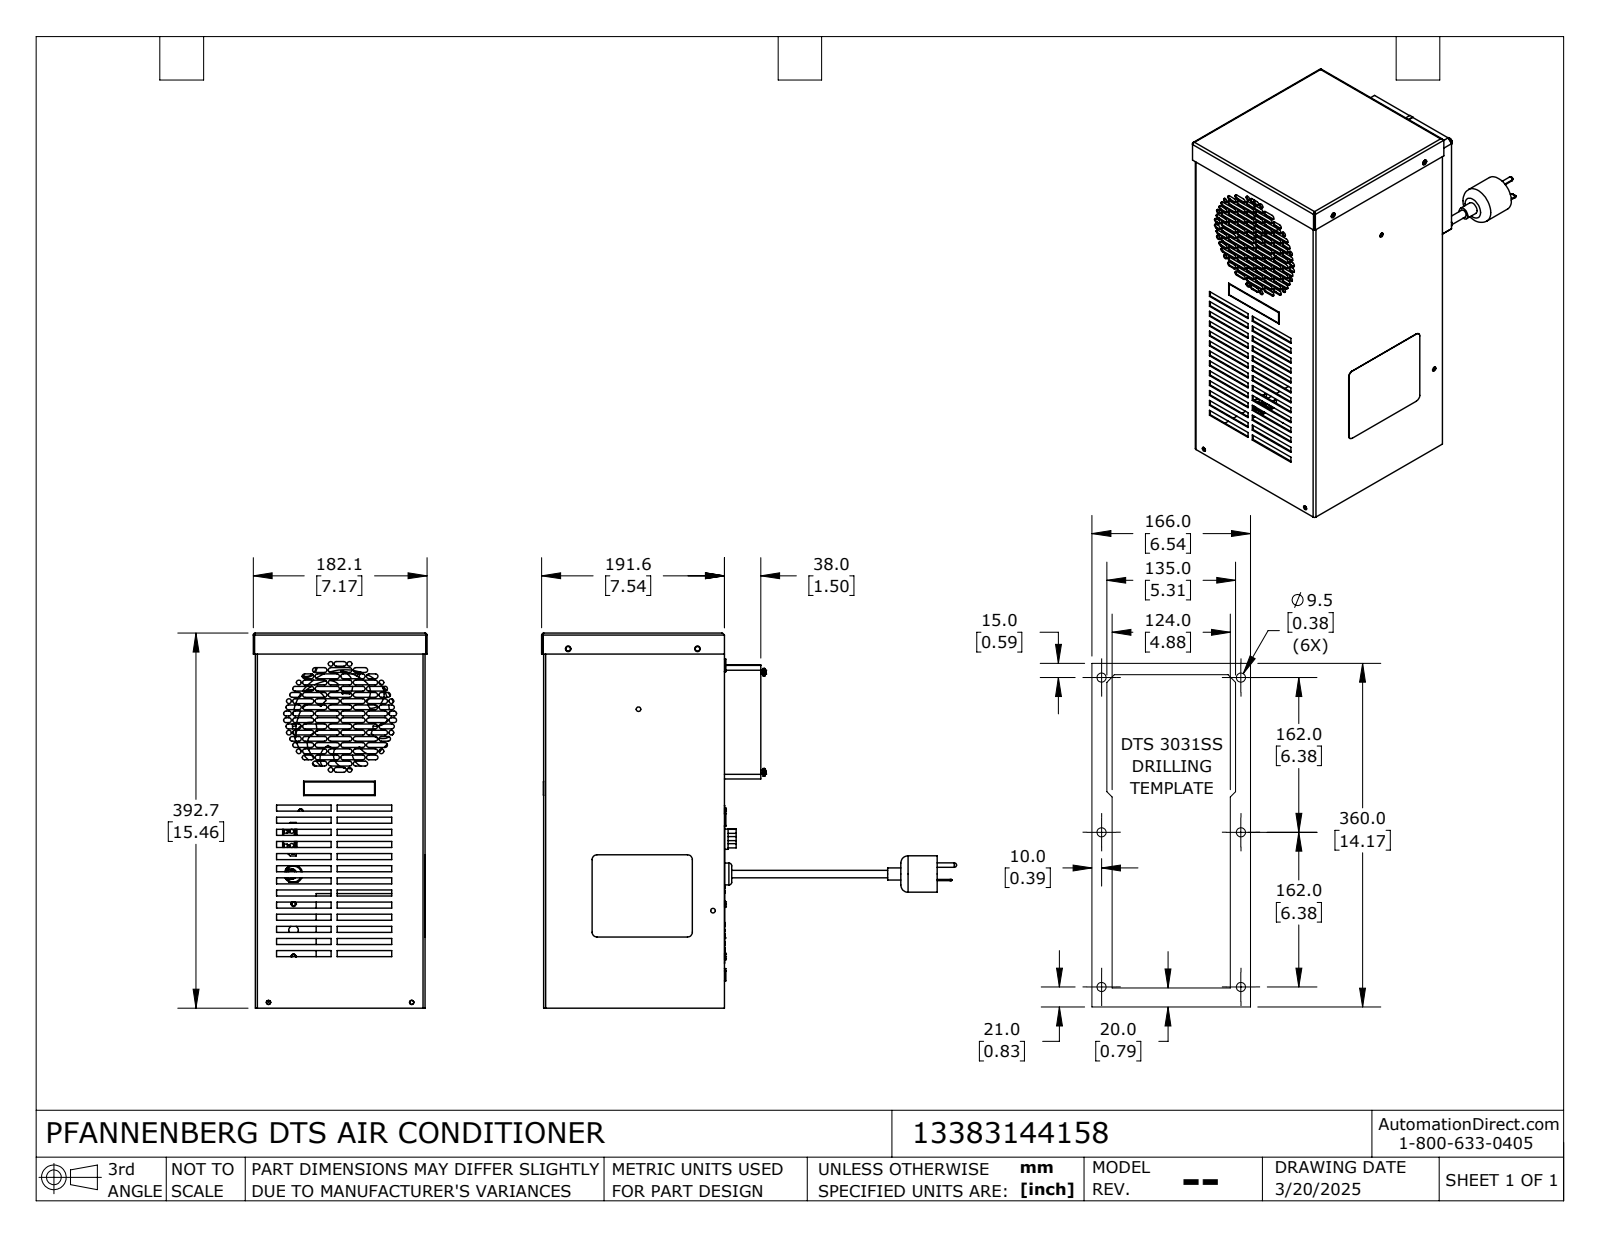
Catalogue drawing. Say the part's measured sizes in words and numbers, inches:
The part is named "13383144158_Default". Its 3-D file was written by "SolidWorks 2024 (CONFIG_CONTROL_DESIGN)". It is 28 solids with 3064 faces: 1547 planar, 697 cylindrical and 820 other. Overall it measures 17.116 by 15.461 by 7.168 inches. Its volume is 53.71 cubic inches and its surface area 1 449 square inches. Round holes: 17 of diameter 0.197, 9 of diameter 0.165, 9 of diameter 0.177, 6 of diameter 0.283, 5 of diameter 0.189, 5 of diameter 0.194, 3 of diameter 0.091, 3 of diameter 0.142, 3 of diameter 0.157, 3 of diameter 0.169, 2 of diameter 0.067, 2 of diameter 0.125. Round bosses or shafts: 6 of diameter 0.512, 4 of diameter 0.315, 3 of diameter 0.272, 3 of diameter 0.157, 2 of diameter 0.5, 1 of diameter 2.362, 1 of diameter 1.5, 1 of diameter 0.9. Partial cylindrical surfaces (rounded edges, fillets, slot ends): 140 of radius 0.098, 12 of radius 0.02, 8 of radius 0.036, 8 of radius 0.084, 7 of radius 0.039, 7 of radius 0.547, 7 of radius 0.597, 7 of radius 2.224. The main face-to-face distances are 0.048, 6.952, 7.41, 0.083, 6.87, 7, 6.905, 7.362, 7.457, 6.917. The hole center spacings are 0.291, 2.917, 4.126, 8.586, 5.748, 6.378, 0.295, 0.583.
